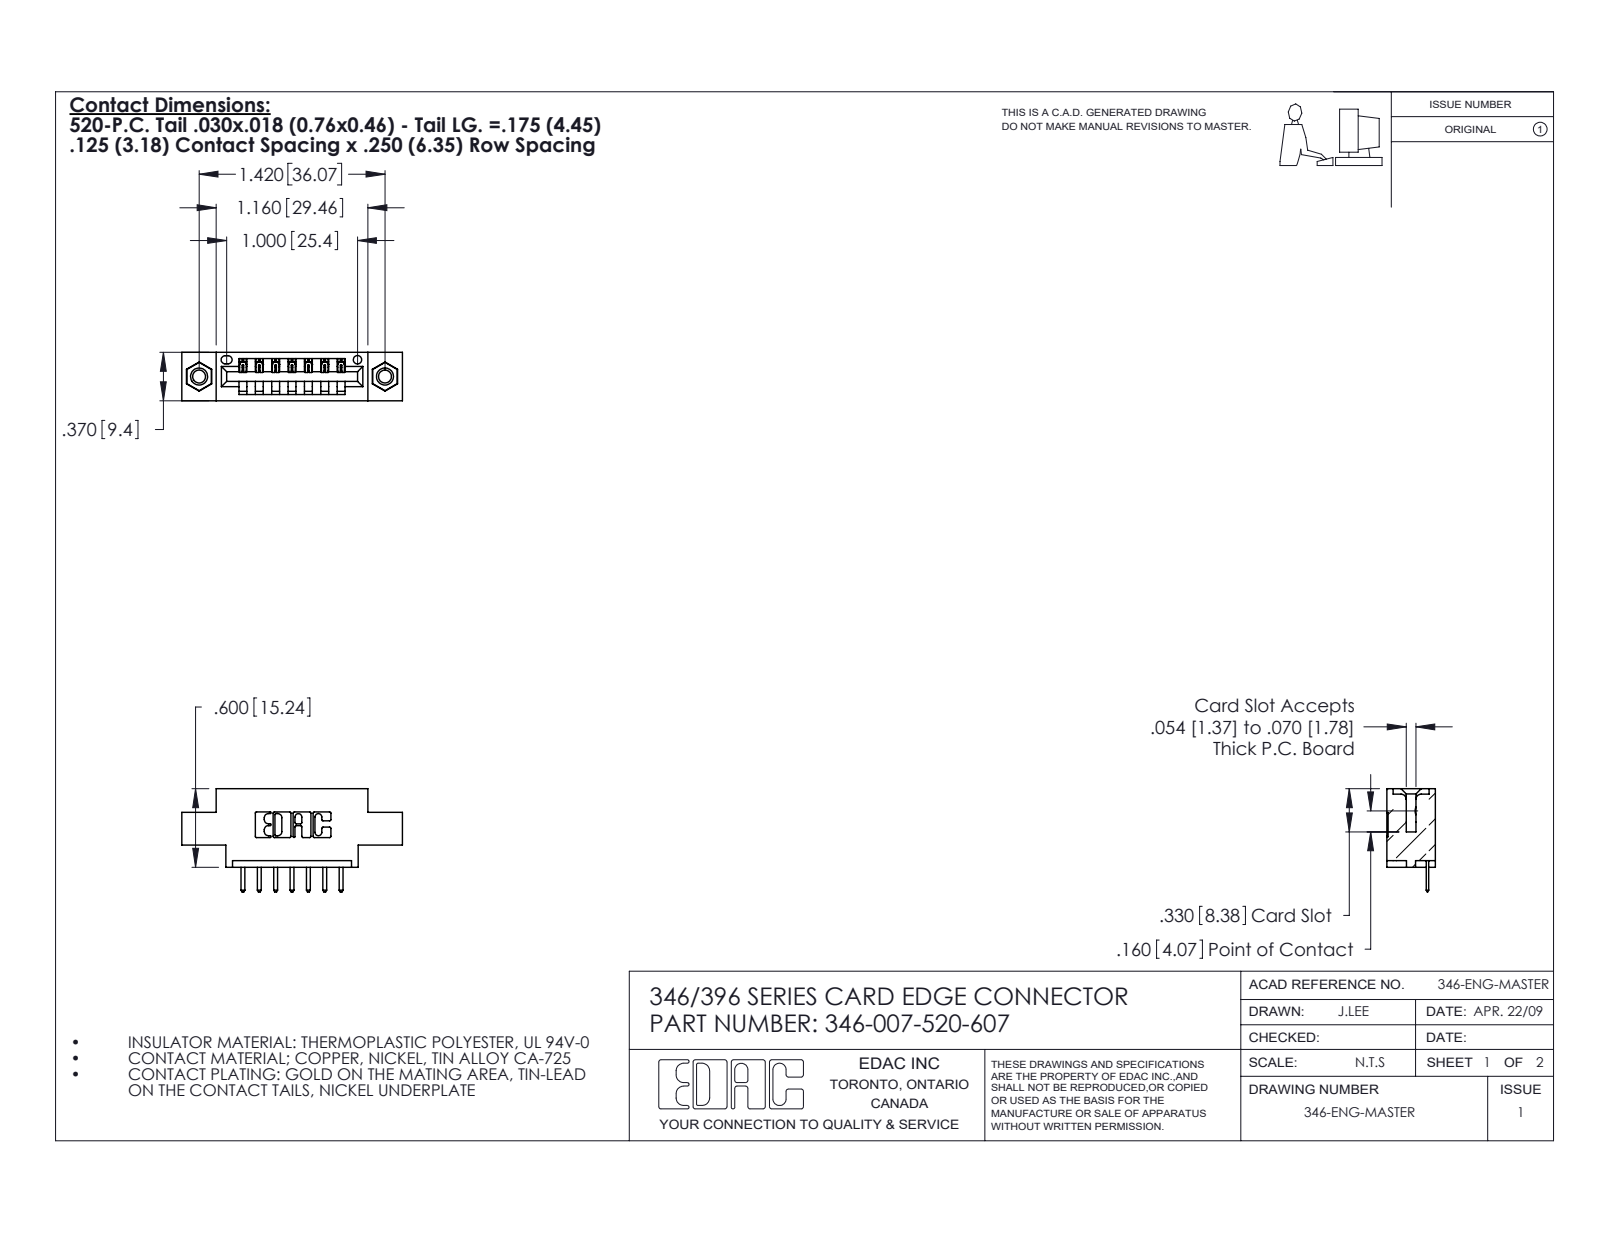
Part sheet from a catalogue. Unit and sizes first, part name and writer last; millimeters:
Units: millimetres
Overall size (bounding box): 42.8 × 20 × 9.4
Round holes (diameter × count): ⌀2.5 ×2, ⌀3.2 ×2, ⌀4 ×2, ⌀1.6 ×1
Round bosses / shafts (diameter × count): ⌀3.9 ×2
Partial cylindrical surfaces — rounded edges, fillets, slot ends (radius × count): R0.3 ×22, R0.3 ×16, R0.2 ×14, R0.2 ×6, R0.8 ×6, R0.7 ×3, R0.8 ×2, R1 ×2
Main face-to-face distances: 6.4, 9.4, 1.2, 8.2, 5.6, 3.8, 2.5, 4.4, 3.2, 4.7
Hole centre spacings: 6.2, 30.9, 36.1
Volume: 3 670 mm³ · Surface area: 4 334 mm²
Bodies: 10 solids, 620 faces (406 planar, 198 cylindrical, 16 other)
Part name (STEP PRODUCT): 345-292-001_345-293-120; 346 Part_0.170 Offset - 0.156 Dia-TI; 345-250-001_345-250-005-103; 346-007-520-607
STEP written by: SolidWorks 2020 (CONFIG_CONTROL_DESIGN)
